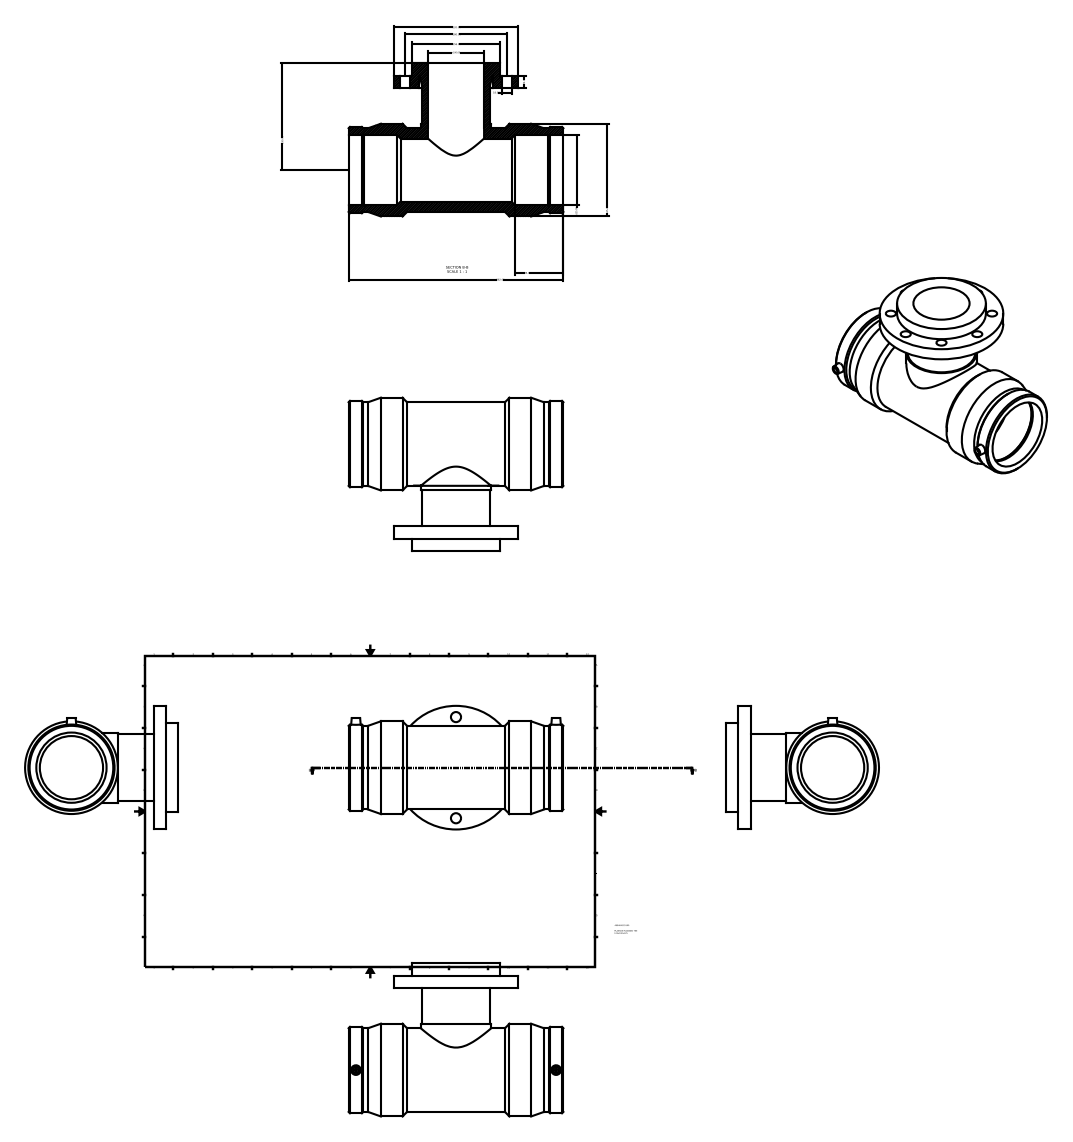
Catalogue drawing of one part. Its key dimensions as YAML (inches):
part_name: "499404125100"
step_written_by: "Autodesk Inventor 2015 (AUTOMOTIVE_DESIGN)"
units: inches
bodies: {solids: 1, faces: 60, planar: 14, cylindrical: 30, other: 16}
overall_size: [15.039, 10.728, 8.661]
volume: 238.6
surface_area: 791.7
round_holes:
  - {diameter: 0.709, count: 8}
  - {diameter: 0.394, count: 2}
  - {diameter: 3.937, count: 1}
  - {diameter: 4.429, count: 1}
  - {diameter: 4.921, count: 1}
  - {diameter: 5.118, count: 1}
round_bosses_or_shafts:
  - {diameter: 0.157, count: 2}
  - {diameter: 8.661, count: 1}
  - {diameter: 6.496, count: 1}
  - {diameter: 6.22, count: 1}
  - {diameter: 6.041, count: 1}
  - {diameter: 5.86, count: 1}
  - {diameter: 5.846, count: 1}
  - {diameter: 4.921, count: 1}
face_to_face_distances: [0.866, 1.732, 15.039, 4.232, 3.366, 2.5, 1.064, 13.976, 12.912, 0.551]
hole_center_spacings: [2.712, 3.543, 5.011, 6.547, 7.087, 14.024]
